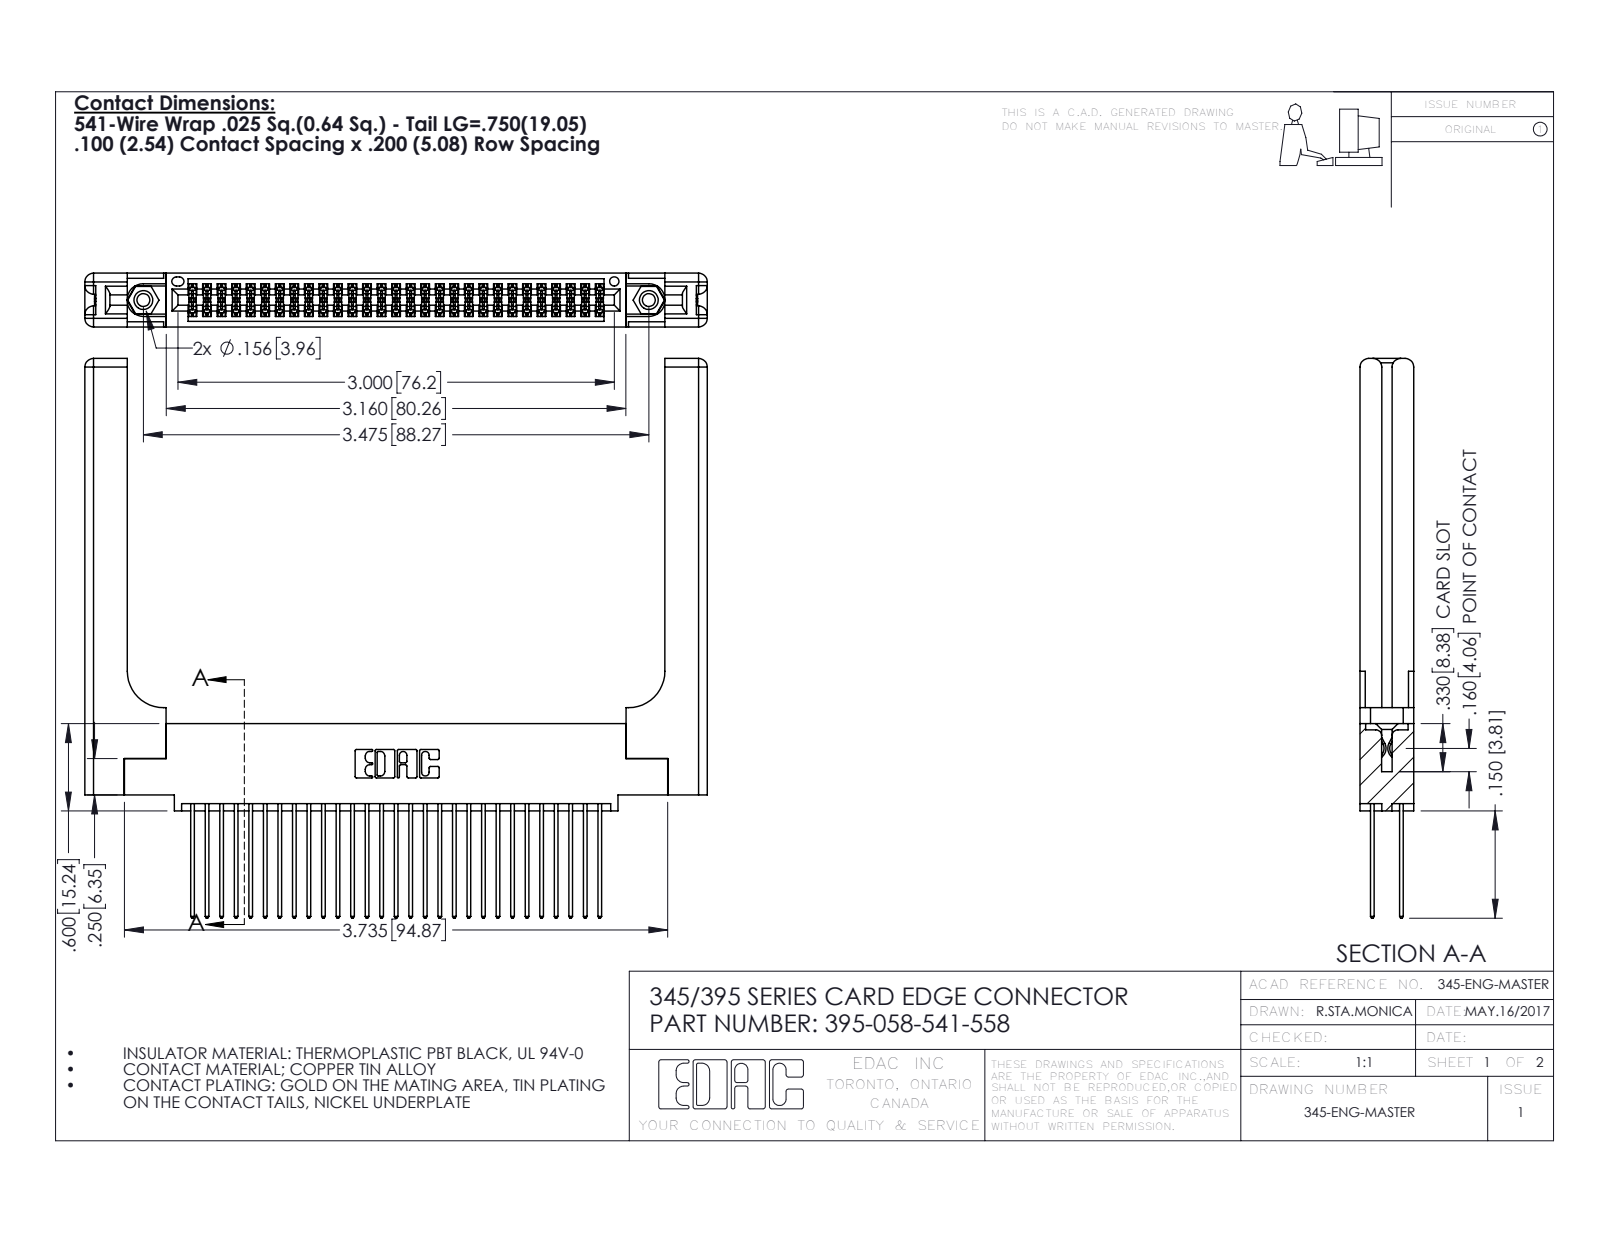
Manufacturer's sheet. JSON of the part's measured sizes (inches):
{"part_name": "395-058-541-558; 345-292-001_345-293-141; 345-220-058_345-220-058; 345-250-001_345-250-001-102 (+1 more)", "step_written_by": "SolidWorks 2016 (CONFIG_CONTROL_DESIGN)", "units": "inches", "bodies": {"solids": 63, "faces": 3286, "planar": 2146, "cylindrical": 1080, "other": 60}, "overall_size": [4.279, 3.847, 0.37], "volume_in3": 1.17, "surface_area_in2": 34.53, "round_holes": [[0.089, 2], [0.125, 2], [0.156, 2], [0.064, 1]], "round_bosses_or_shafts": [[0.155, 2]], "partial_cylinders_radius": [[0.006, 87], [0.01, 58], [0.01, 22], [0.06, 16], [0.007, 6], [0.031, 6], [0.026, 3], [0.014, 2]], "face_to_face_distances": [0.072, 0.298, 0.37, 0.098, 0.272, 0.025, 0.2, 0.225, 0.148, 0.15], "hole_center_spacings": [0.27, 3.24, 3.475]}
